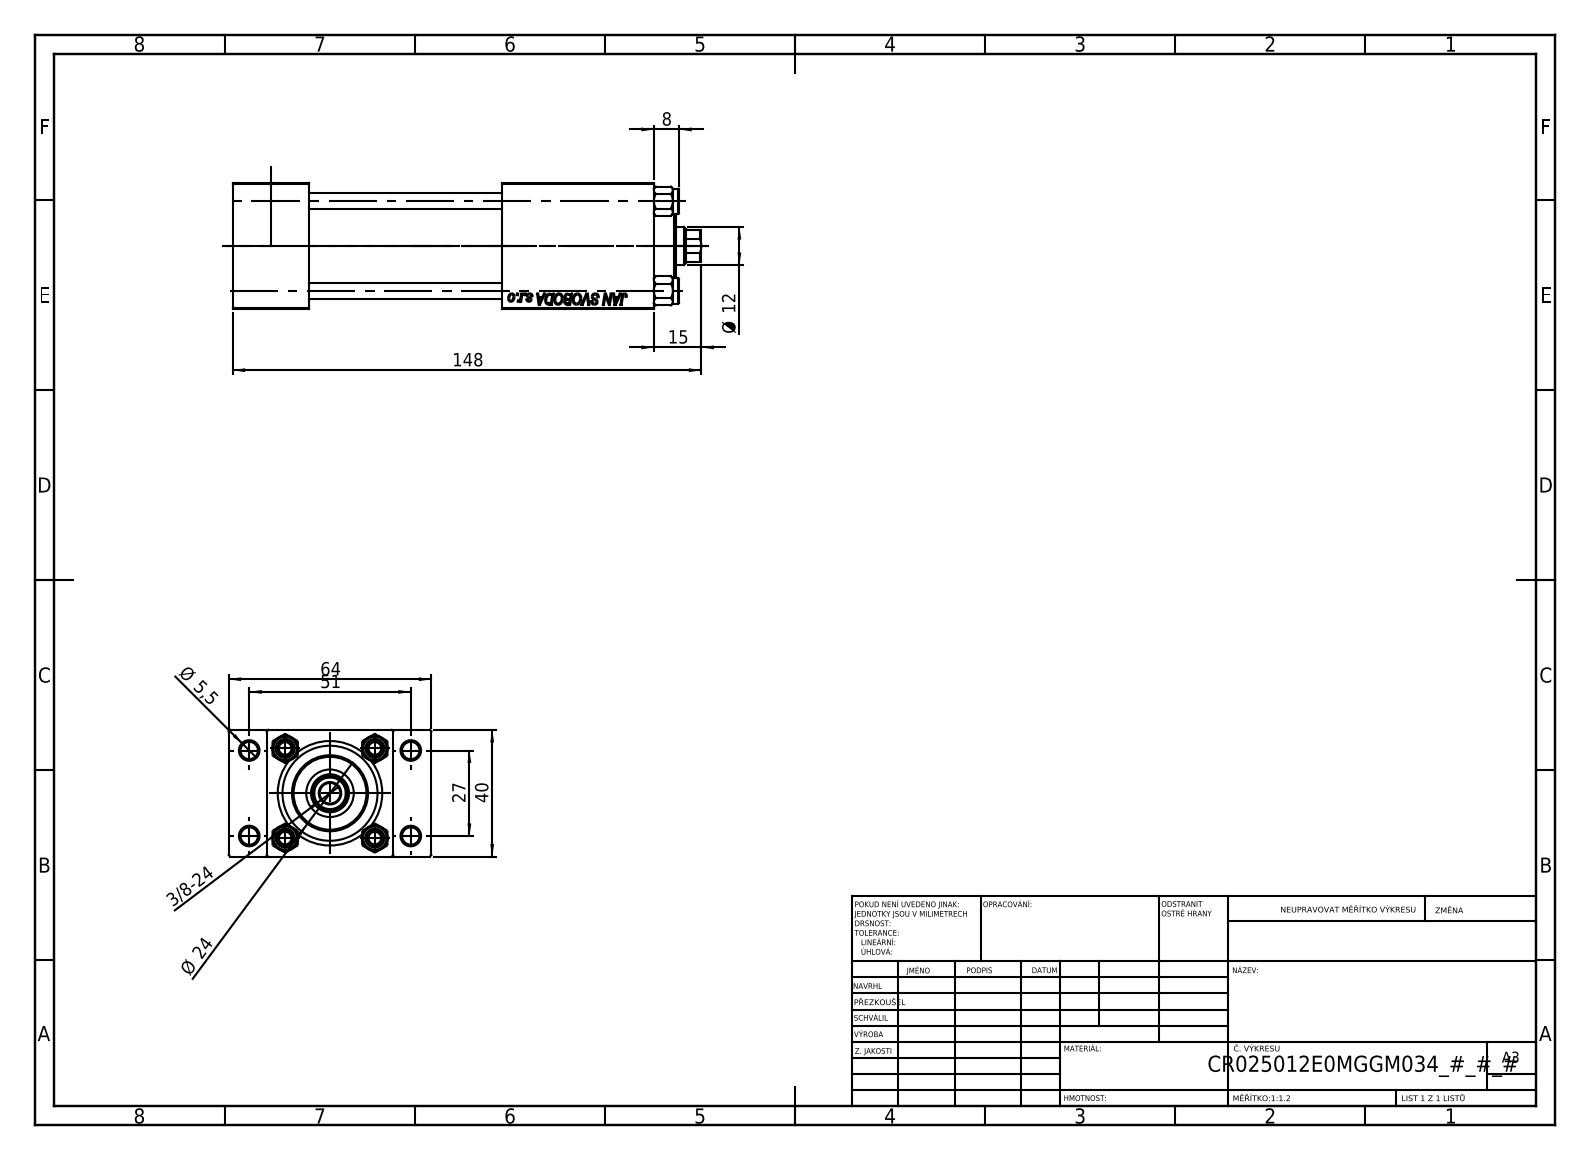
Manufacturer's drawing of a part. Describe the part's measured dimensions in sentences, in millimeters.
The part is named "V215CR_TYCINKA_E; NUT_M5_E; V215CR_VCP_E; V215CR_E_Body (+1 more)". Its 3-D file was written by "SolidWorks 2019 (CONFIG_CONTROL_DESIGN)". It is 11 solids with 1136 faces: 497 planar, 87 cylindrical and 552 other. Overall it measures 148 by 64 by 40 millimeters. Its volume is 170 292 cubic millimeters and its surface area 65 975 square millimeters. Round holes: 4 of diameter 5, 4 of diameter 5.5, 3 of diameter 20, 2 of diameter 7, 2 of diameter 13.16, 1 of diameter 6.5, 1 of diameter 12, 1 of diameter 15, 1 of diameter 25, 1 of diameter 30. Round bosses or shafts: 4 of diameter 8, 1 of diameter 31, 1 of diameter 24. Partial cylindrical surfaces (rounded edges, fillets, slot ends): 1 of radius 5.5. The main face-to-face distances are 40, 24, 12, 52, 133, 109, 104.3, 80.3, 28.7, 64. The hole center spacings are 11.37, 20.01, 28.3, 28.85, 29.89, 39.66, 48.34, 27.
